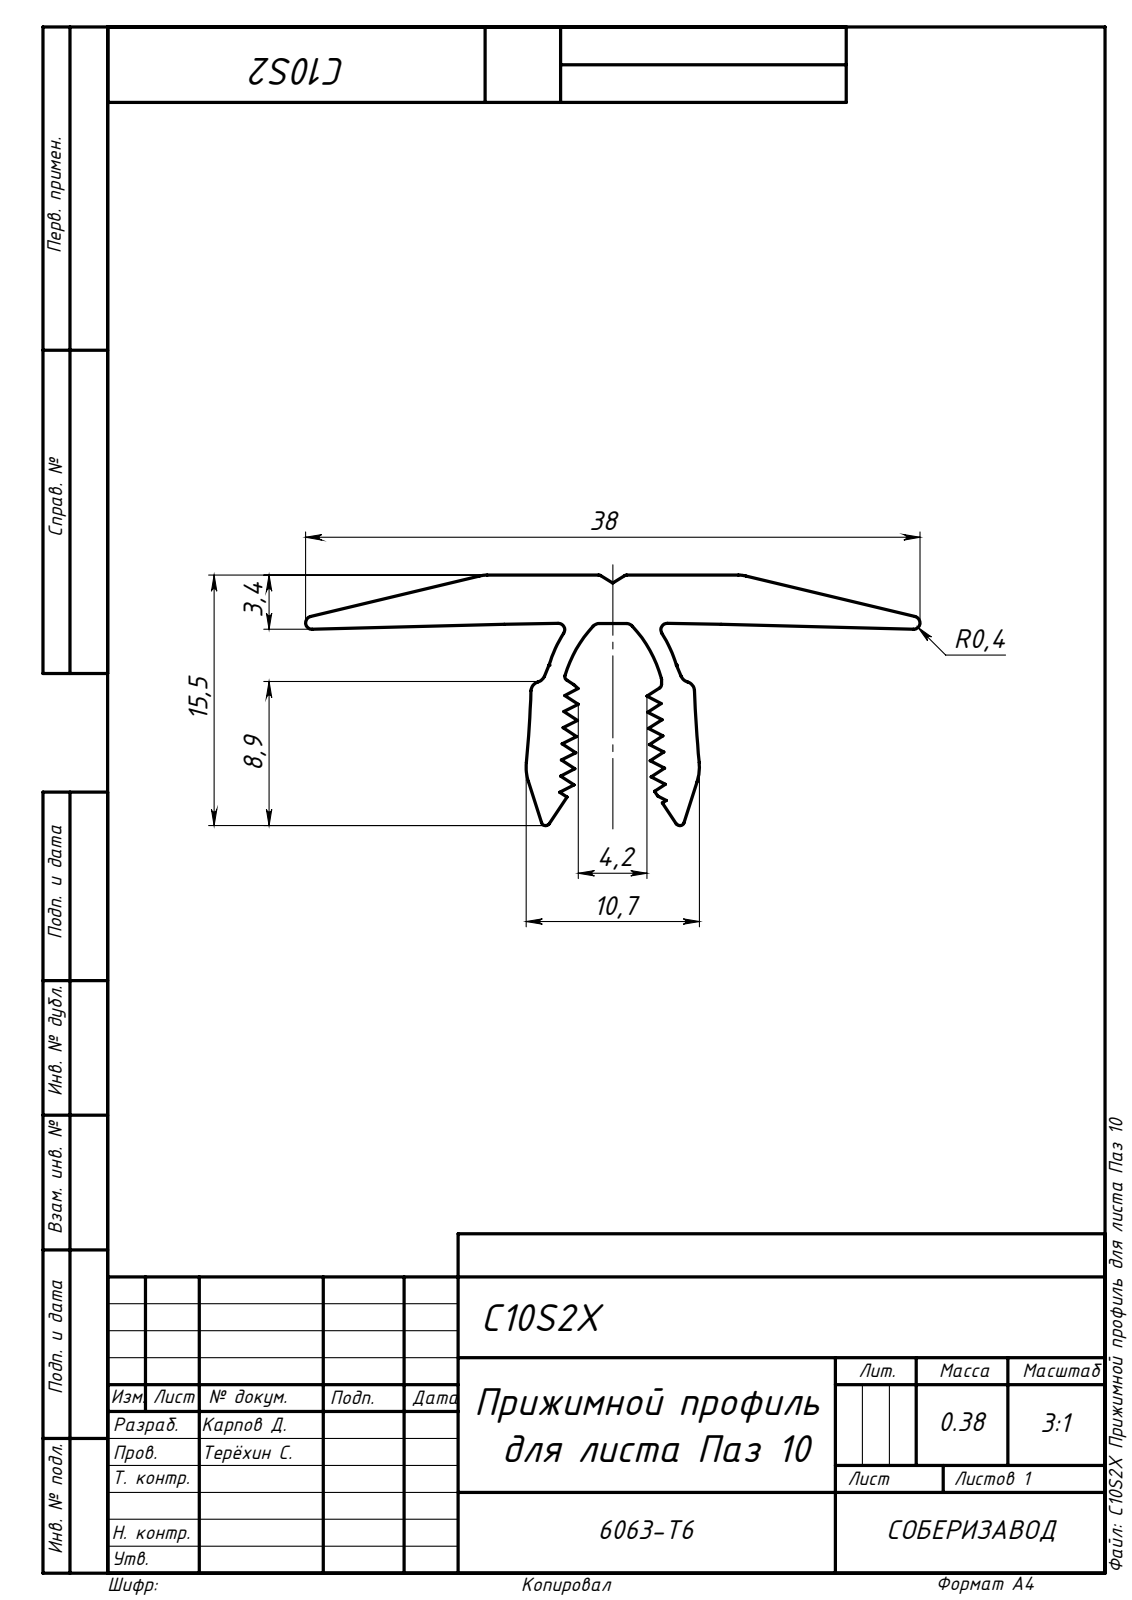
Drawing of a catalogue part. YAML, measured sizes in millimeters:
part_name: "C10S2X Прижимной профиль для листа Паз 10"
step_written_by: "SolidWorks 2019 (AUTOMOTIVE_DESIGN)"
units: millimeters
bodies: {solids: 1, faces: 87, planar: 54, cylindrical: 33, other: 0}
overall_size: [1000, 38, 15.5]
volume: 138996
surface_area: 141930
partial_cylinders:
  - {radius: 0.25, count: 9}
  - {radius: 0.4, count: 4}
  - {radius: 0.6, count: 4}
  - {radius: 0.5, count: 2}
  - {radius: 0.67, count: 2}
  - {radius: 2, count: 2}
  - {radius: 3, count: 2}
  - {radius: 7.84, count: 2}
face_to_face_distances: [1.73, 0.87, 2.6, 0.86, 4.33, 3.46, 3.47, 1.74, 2.59, 5.19]
